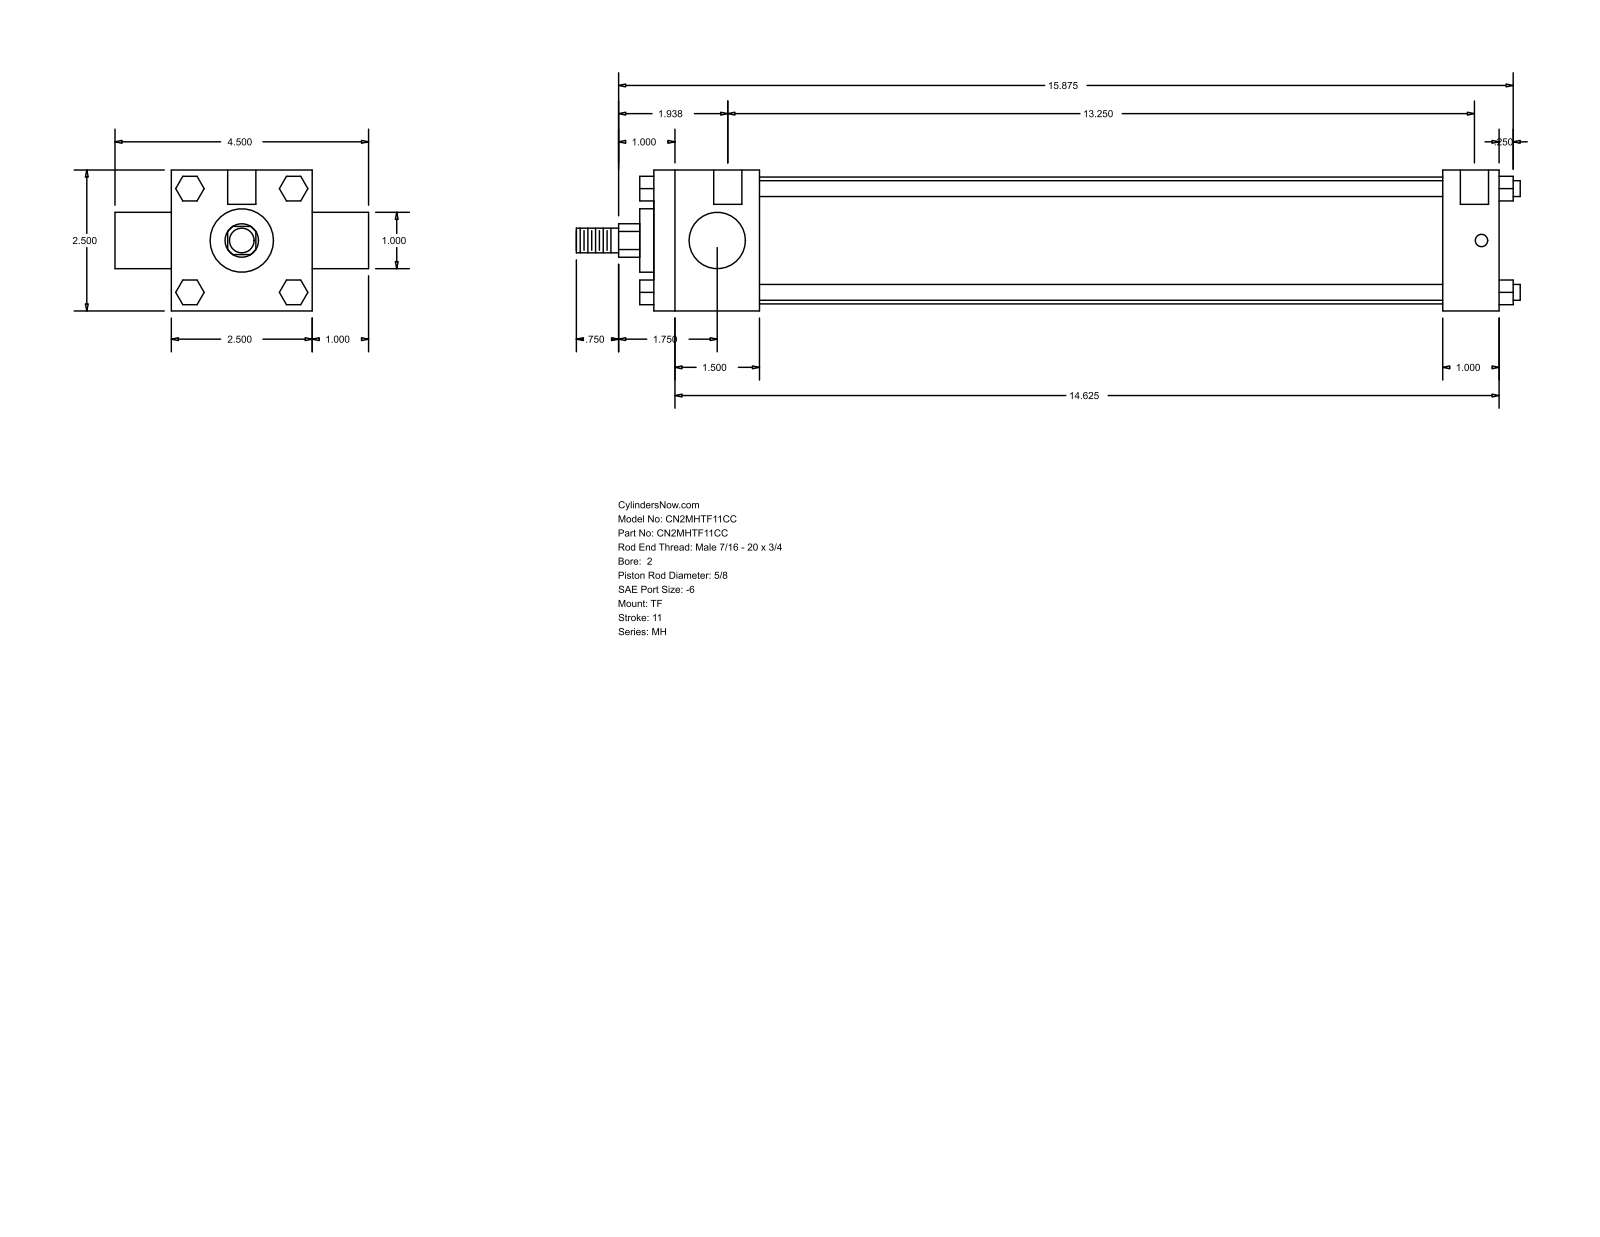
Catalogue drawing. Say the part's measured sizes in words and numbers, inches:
The part is named "MH_TF__0200_0.625". Its 3-D file was written by "GSSL Pune (CONFIG_CONTROL_DESIGN)". It is 0 solids with 120 faces: 92 planar, 28 cylindrical and 0 other. Overall it measures 16.75 by 4.5 by 2.5 inches. Round holes: 3 of diameter 0.219, 2 of diameter 0.5. Round bosses or shafts: 4 of diameter 0.281, 1 of diameter 2.25, 1 of diameter 1.125, 1 of diameter 1, 1 of diameter 0.625, 1 of diameter 0.437. Partial cylindrical surfaces (rounded edges, fillets, slot ends): 1 of radius 0.297. The main face-to-face distances are 2.5, 15, 1, 1.875, 14, 12.125, 13.125, 0.25, 3.5, 15.25. The hole center spacings are 0.125, 0.187, 13.25, 13.375, 13.437, 13.563.
